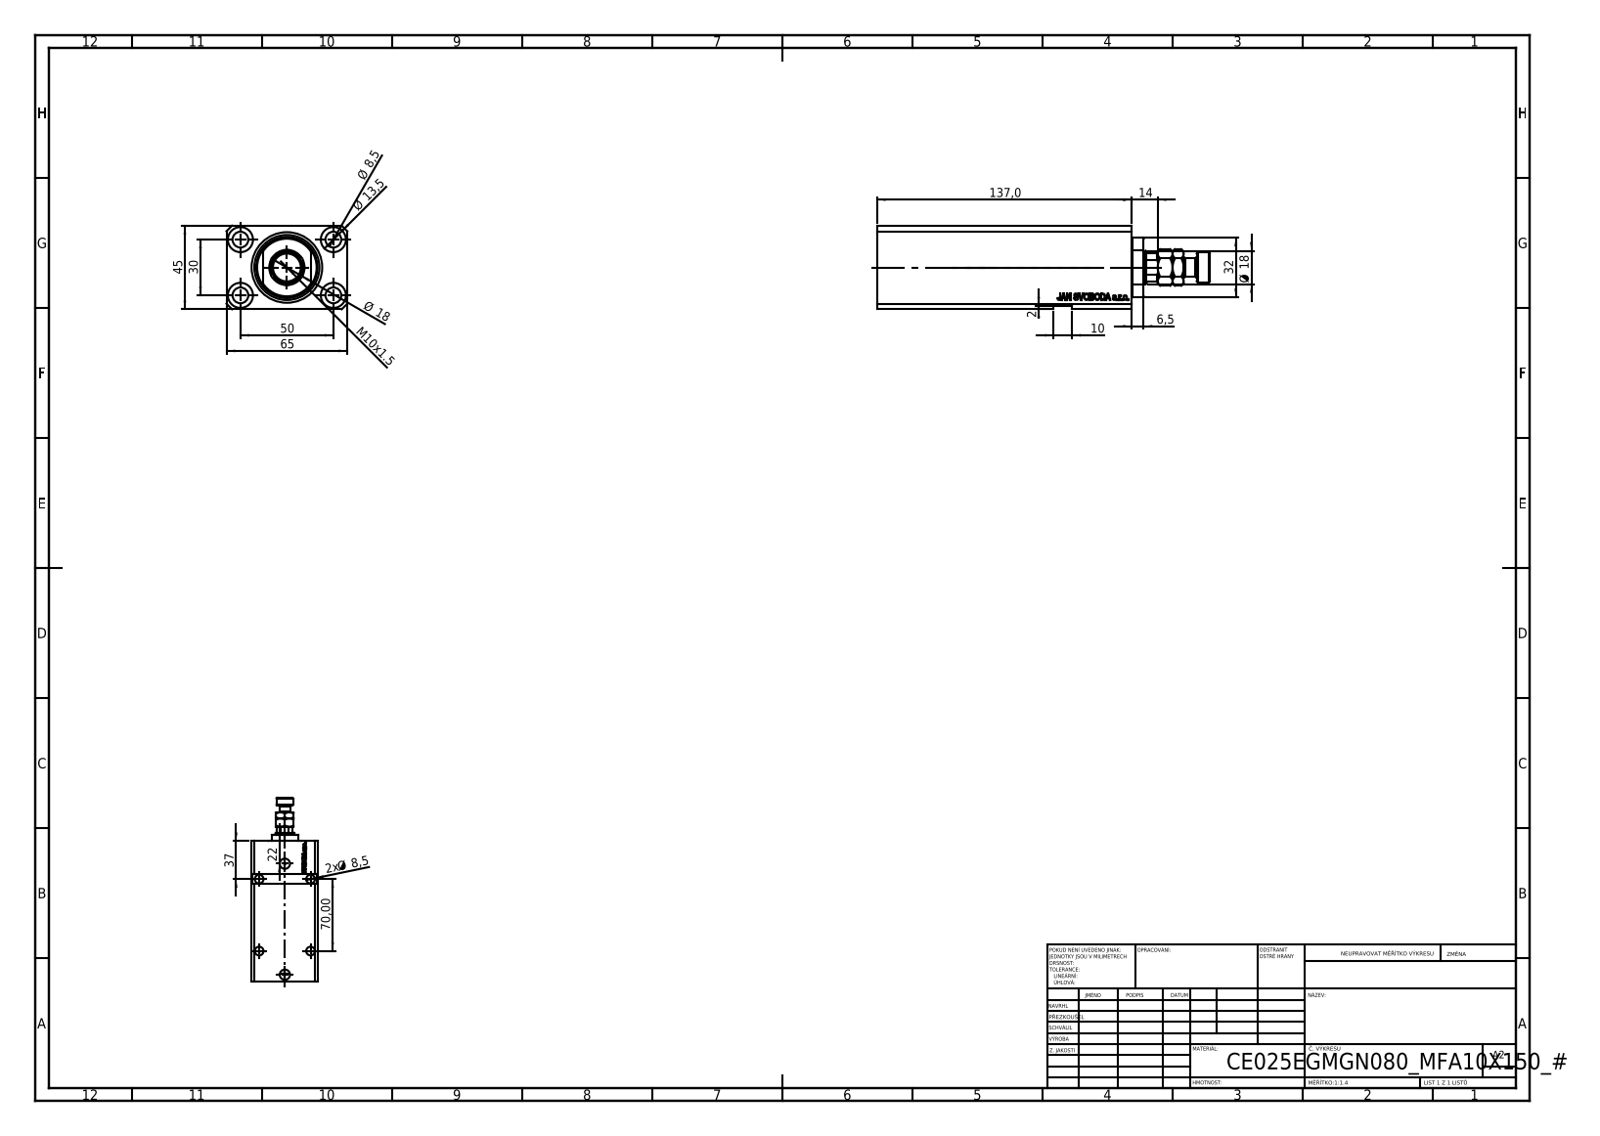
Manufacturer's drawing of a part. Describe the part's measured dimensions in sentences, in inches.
The part is named "V250CE_C_VCP; V250CE_VC_E; V250CE_E_Body; MFA". Its 3-D file was written by "SolidWorks 2019 (CONFIG_CONTROL_DESIGN)". It is 4 solids with 969 faces: 451 planar, 108 cylindrical and 410 other. Overall it measures 7.047 by 2.559 by 1.772 inches. Its volume is 20.77 cubic inches and its surface area 128.1 square inches. Round holes: 9 of diameter 0.335, 4 of diameter 0.049, 4 of diameter 0.531, 2 of diameter 0.394, 2 of diameter 0.518, 2 of diameter 0.787, 1 of diameter 0.709, 1 of diameter 0.984, 1 of diameter 1.496. Round bosses or shafts: 1 of diameter 0.63, 1 of diameter 0.394. Partial cylindrical surfaces (rounded edges, fillets, slot ends): 1 of radius 0.335, 1 of radius 0.63. The main face-to-face distances are 1.772, 2.559, 0.551, 4.843, 5.394, 0.272, 4.571, 5.122, 1.102, 1.693. The hole center spacings are 1.148, 1.969, 1.181, 1.323, 1.337, 2.296, 2.756, 3.387.
